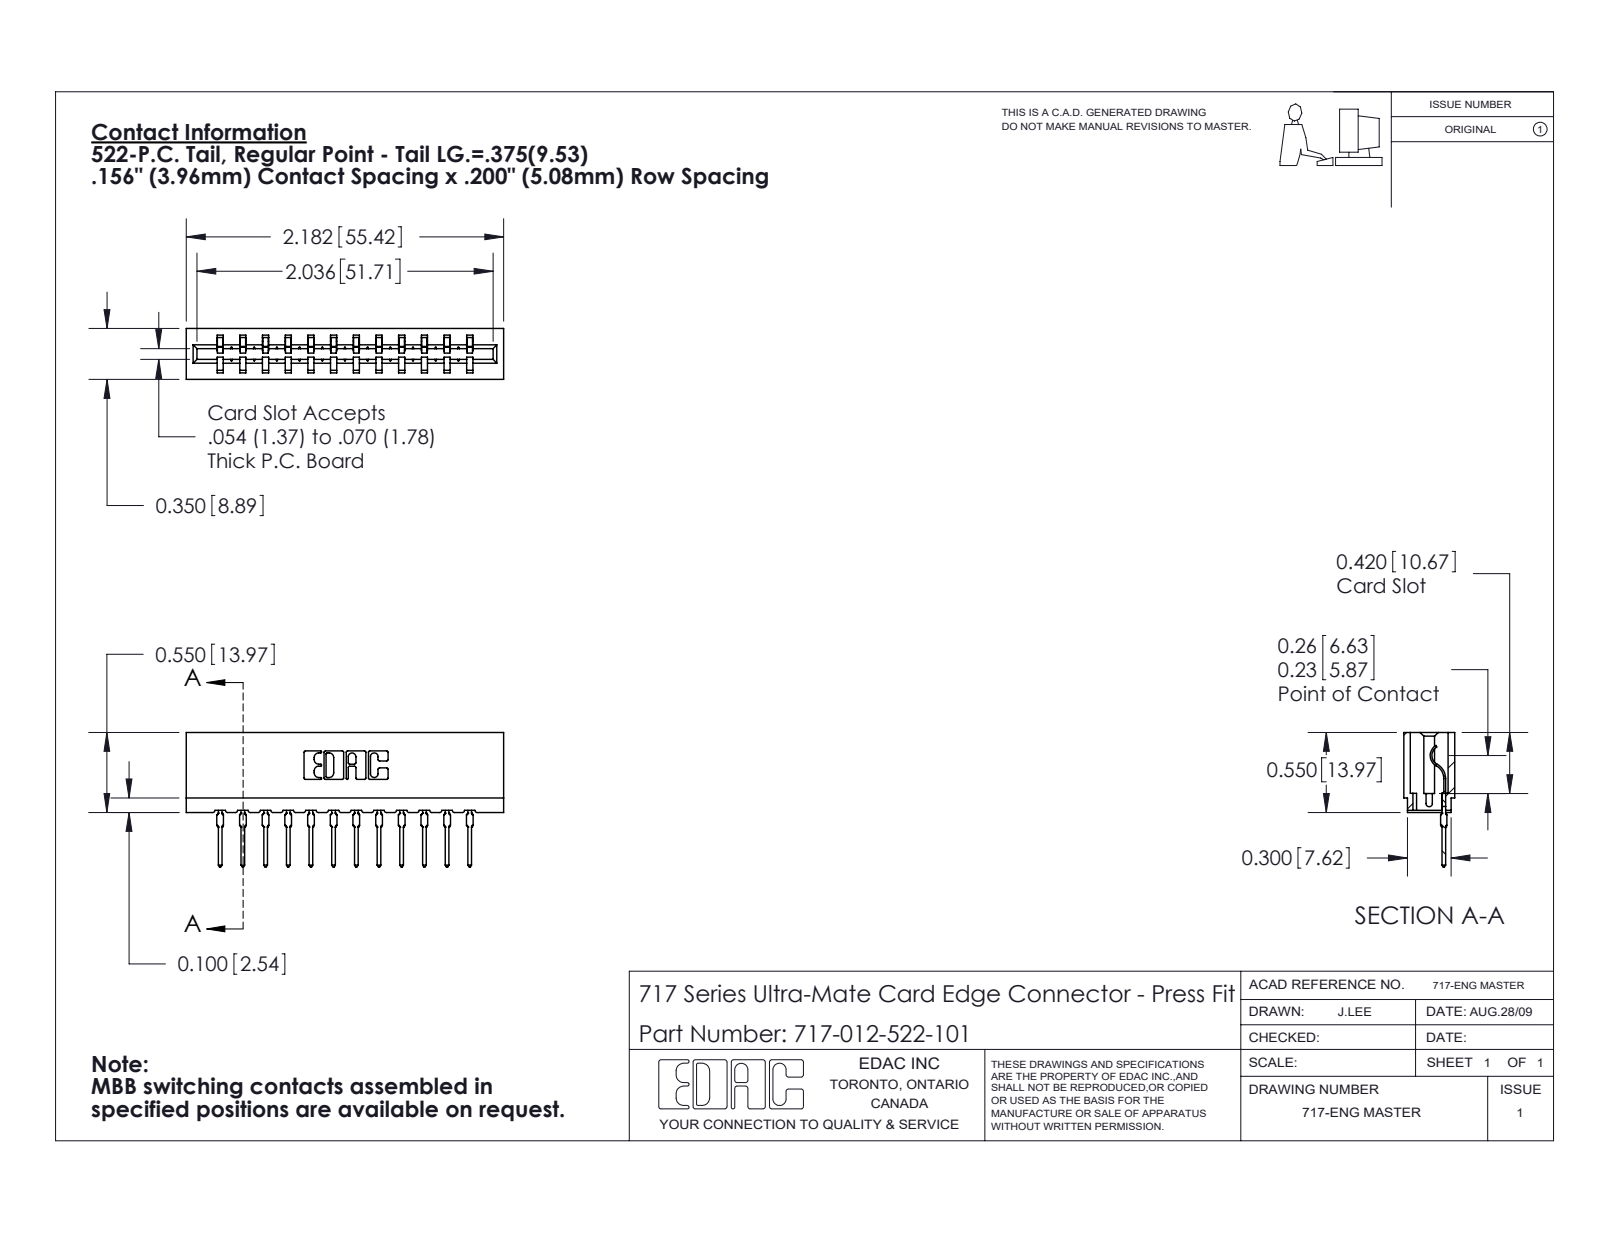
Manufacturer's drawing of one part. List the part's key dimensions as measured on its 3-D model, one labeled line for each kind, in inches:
Part name (STEP PRODUCT): 717-012-522-101; 745-292-001_522; 717 Part_Insulator Option - 06
STEP written by: SolidWorks 2020 (CONFIG_CONTROL_DESIGN)
Units: inches
Bodies: 13 solids, 1450 faces (870 planar, 268 cylindrical, 312 other)
Overall size (bounding box): 2.182 × 0.924 × 0.35
Volume: 0.294 in³ · Surface area: 10.03 in²
Partial cylindrical surfaces — rounded edges, fillets, slot ends (radius × count): R0.015 ×24, R0.021 ×24, R0.01 ×22, R0.007 ×6, R0.031 ×6, R0.005 ×4, R0.011 ×4, R0.026 ×3
Main face-to-face distances: 0.212, 0.138, 0.156, 0.624, 0.35, 0.468, 0.198, 0.312, 0.27, 0.042
